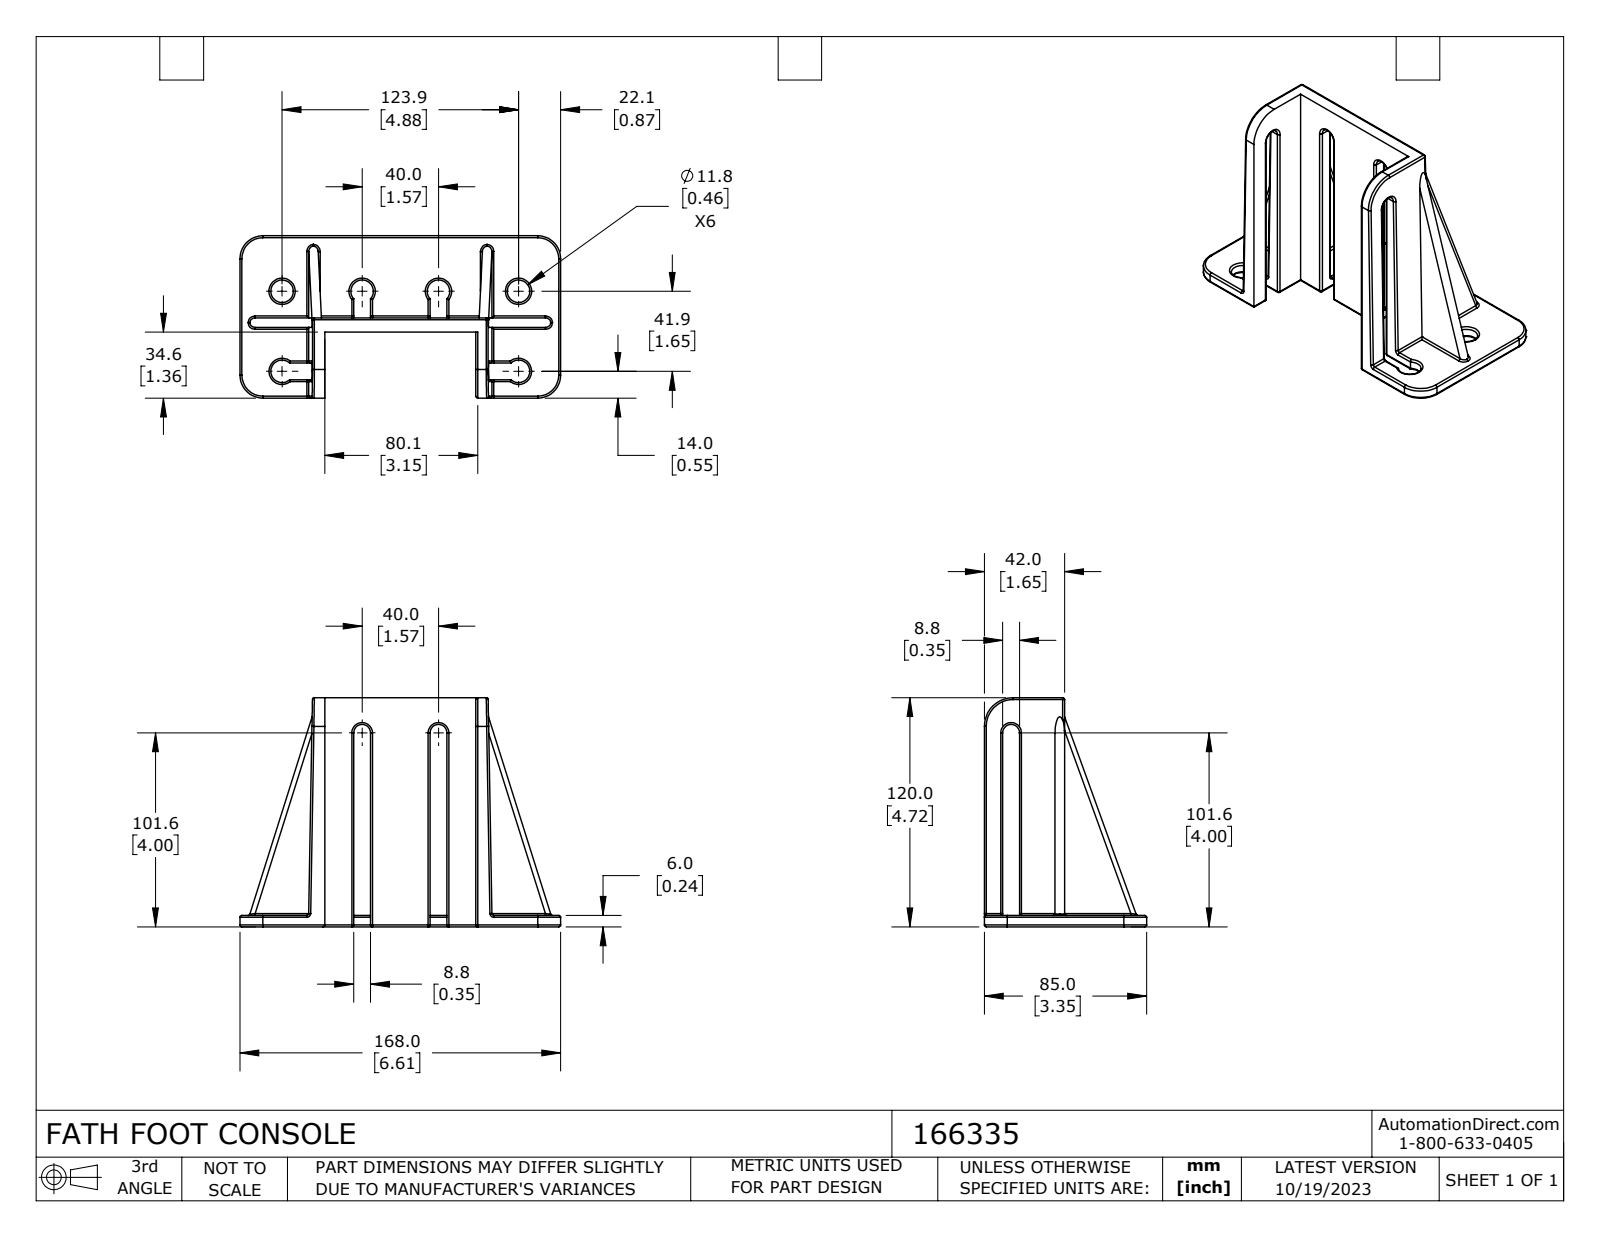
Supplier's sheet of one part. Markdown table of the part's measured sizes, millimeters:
| quantity | value |
| --- | --- |
| part name | 166335 |
| STEP written by | SolidWorks 2023 (CONFIG_CONTROL_DESIGN) |
| units | millimeters |
| bodies | 1 solid, 211 faces (30 planar, 102 cylindrical, 79 other) |
| overall size | 168 × 120 × 85 |
| volume | 206 600 mm³ |
| surface area | 74 390 mm² |
| round holes (diameter × count) | 11.8 × 2 |
| partial cylindrical surfaces (radius × count) | 1 × 54, 2.5 × 4, 5.9 × 4, 12 × 4, 4.4 × 3, 15 × 1 |
| main face-to-face distances | 6, 7.4, 5, 79.1, 2.4, 8.8, 34.5, 37, 42, 9.6 |
| hole center spacings | 123.9 |
